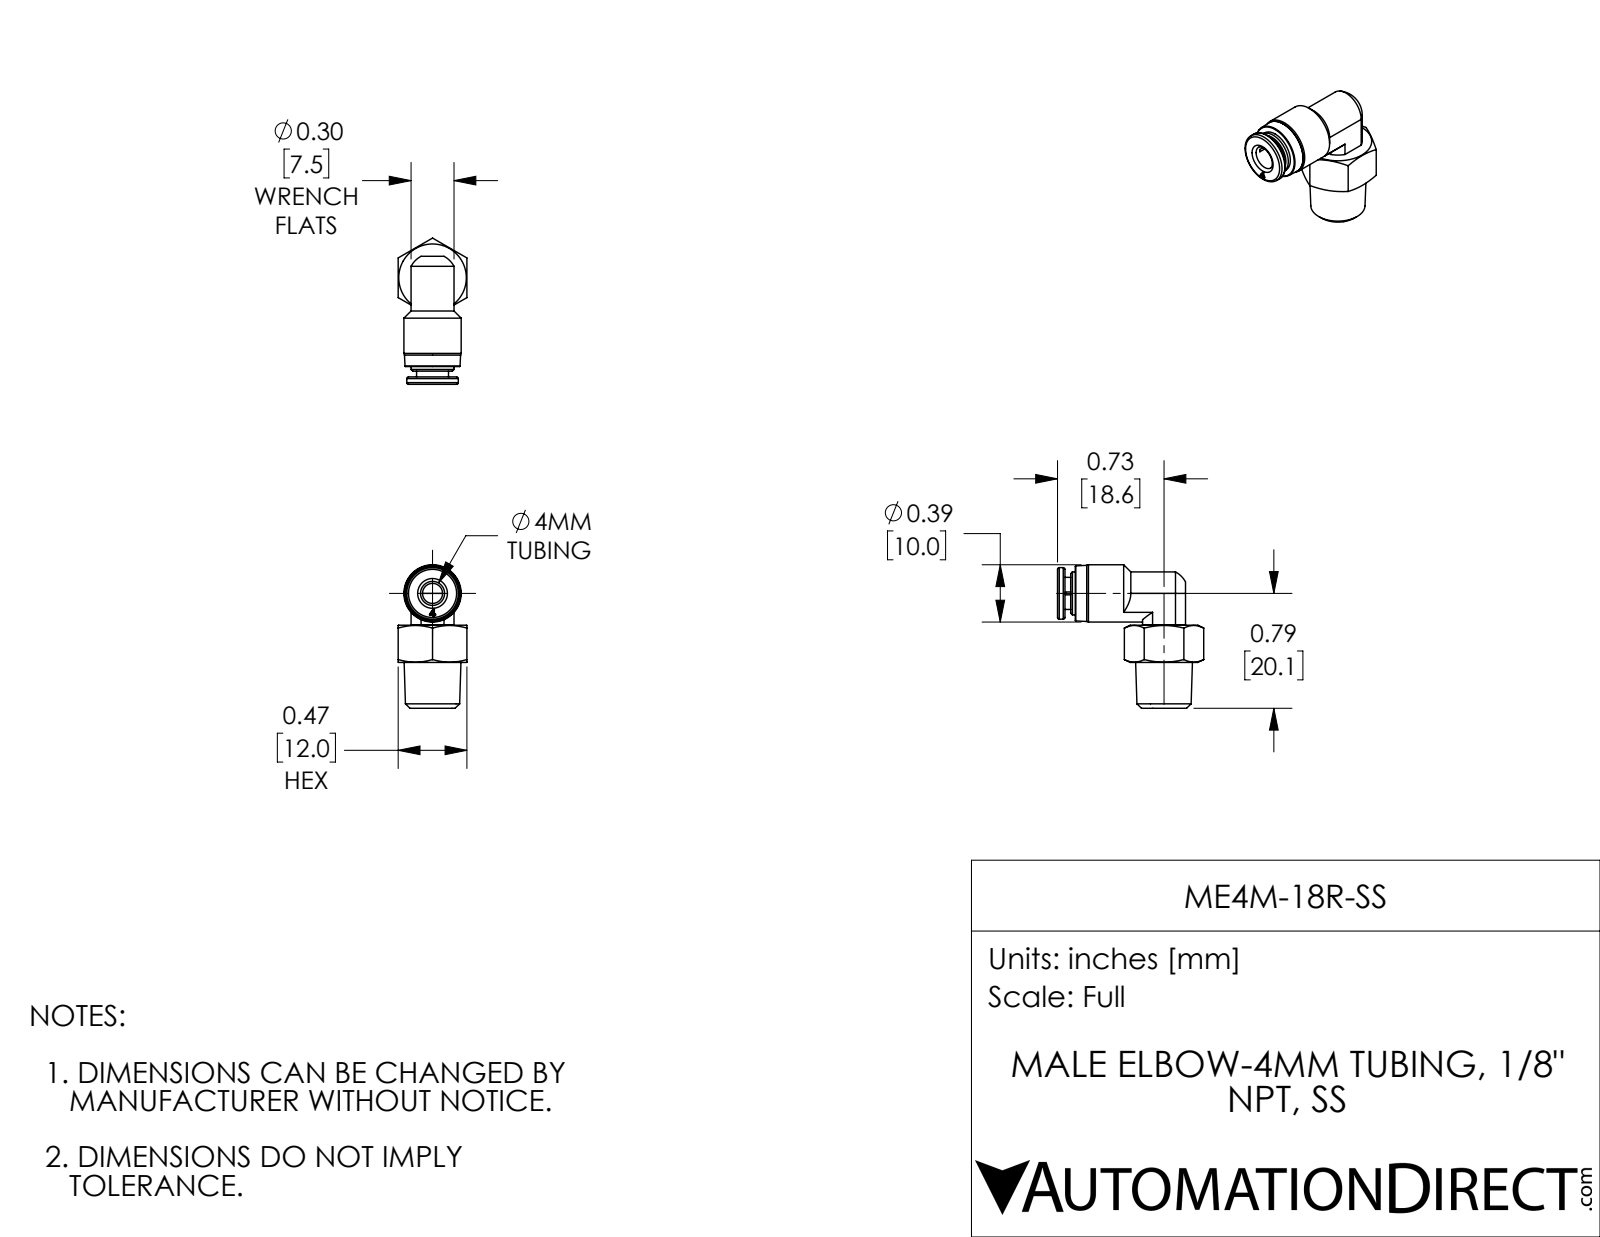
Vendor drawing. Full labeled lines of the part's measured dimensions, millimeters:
Part name (STEP PRODUCT): ME4M-18R-SS
STEP written by: SolidWorks 2017 (AUTOMOTIVE_DESIGN)
Units: millimetres
Bodies: 2 solids, 108 faces (46 planar, 27 cylindrical, 35 other)
Overall size (bounding box): 25.5 × 25 × 12
Volume: 2 330 mm³ · Surface area: 2 312 mm²
Round holes (diameter × count): ⌀3.5 ×2, ⌀4 ×1, ⌀4.2 ×1, ⌀6 ×1
Round bosses / shafts (diameter × count): ⌀10 ×1, ⌀9 ×1, ⌀7.5 ×1, ⌀6 ×1, ⌀5.6 ×1
Partial cylindrical surfaces — rounded edges, fillets, slot ends (radius × count): R4.2 ×1
Main face-to-face distances: 12, 9.8, 2.3, 7.5, 6.5, 1.3, 14.5, 8, 22.4, 21.1
